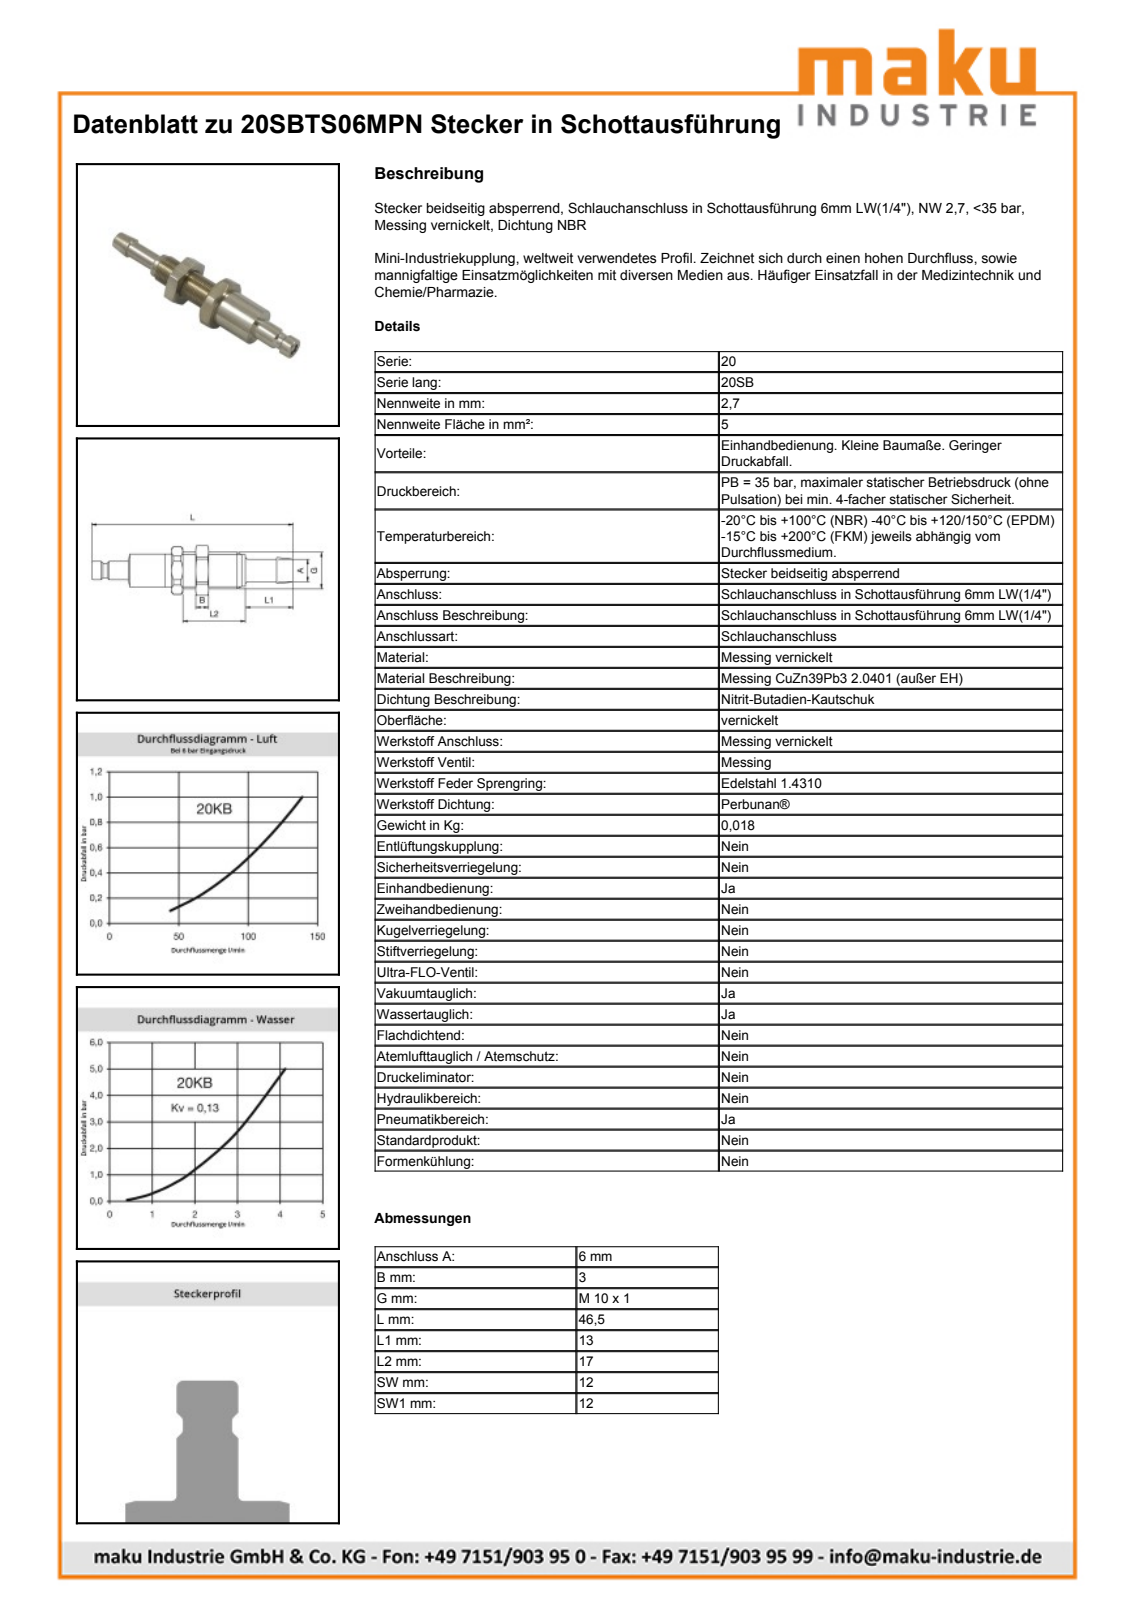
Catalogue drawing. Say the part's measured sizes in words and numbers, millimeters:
The part is named "D113518". Its 3-D file was written by "Autodesk Inventor 2013 (AUTOMOTIVE_DESIGN)". It is 1 solid with 90 faces: 22 planar, 25 cylindrical and 43 other. Overall it measures 53.05 by 13.42 by 12.83 millimeters. Its volume is 2 993 cubic millimeters and its surface area 1 874 square millimeters. Round holes: 1 of diameter 8, 1 of diameter 8.1. Round bosses or shafts: 1 of diameter 10, 1 of diameter 9, 1 of diameter 8.6, 1 of diameter 7.3, 1 of diameter 6.8, 1 of diameter 6.1, 1 of diameter 5, 1 of diameter 3.95. Partial cylindrical surfaces (rounded edges, fillets, slot ends): 1 of radius 6.5, 1 of radius 6.75. The main face-to-face distances are 12, 3.05, 33.05, 30, 8.35, 11.35, 5.3, 8.3, 3, 24.7.
